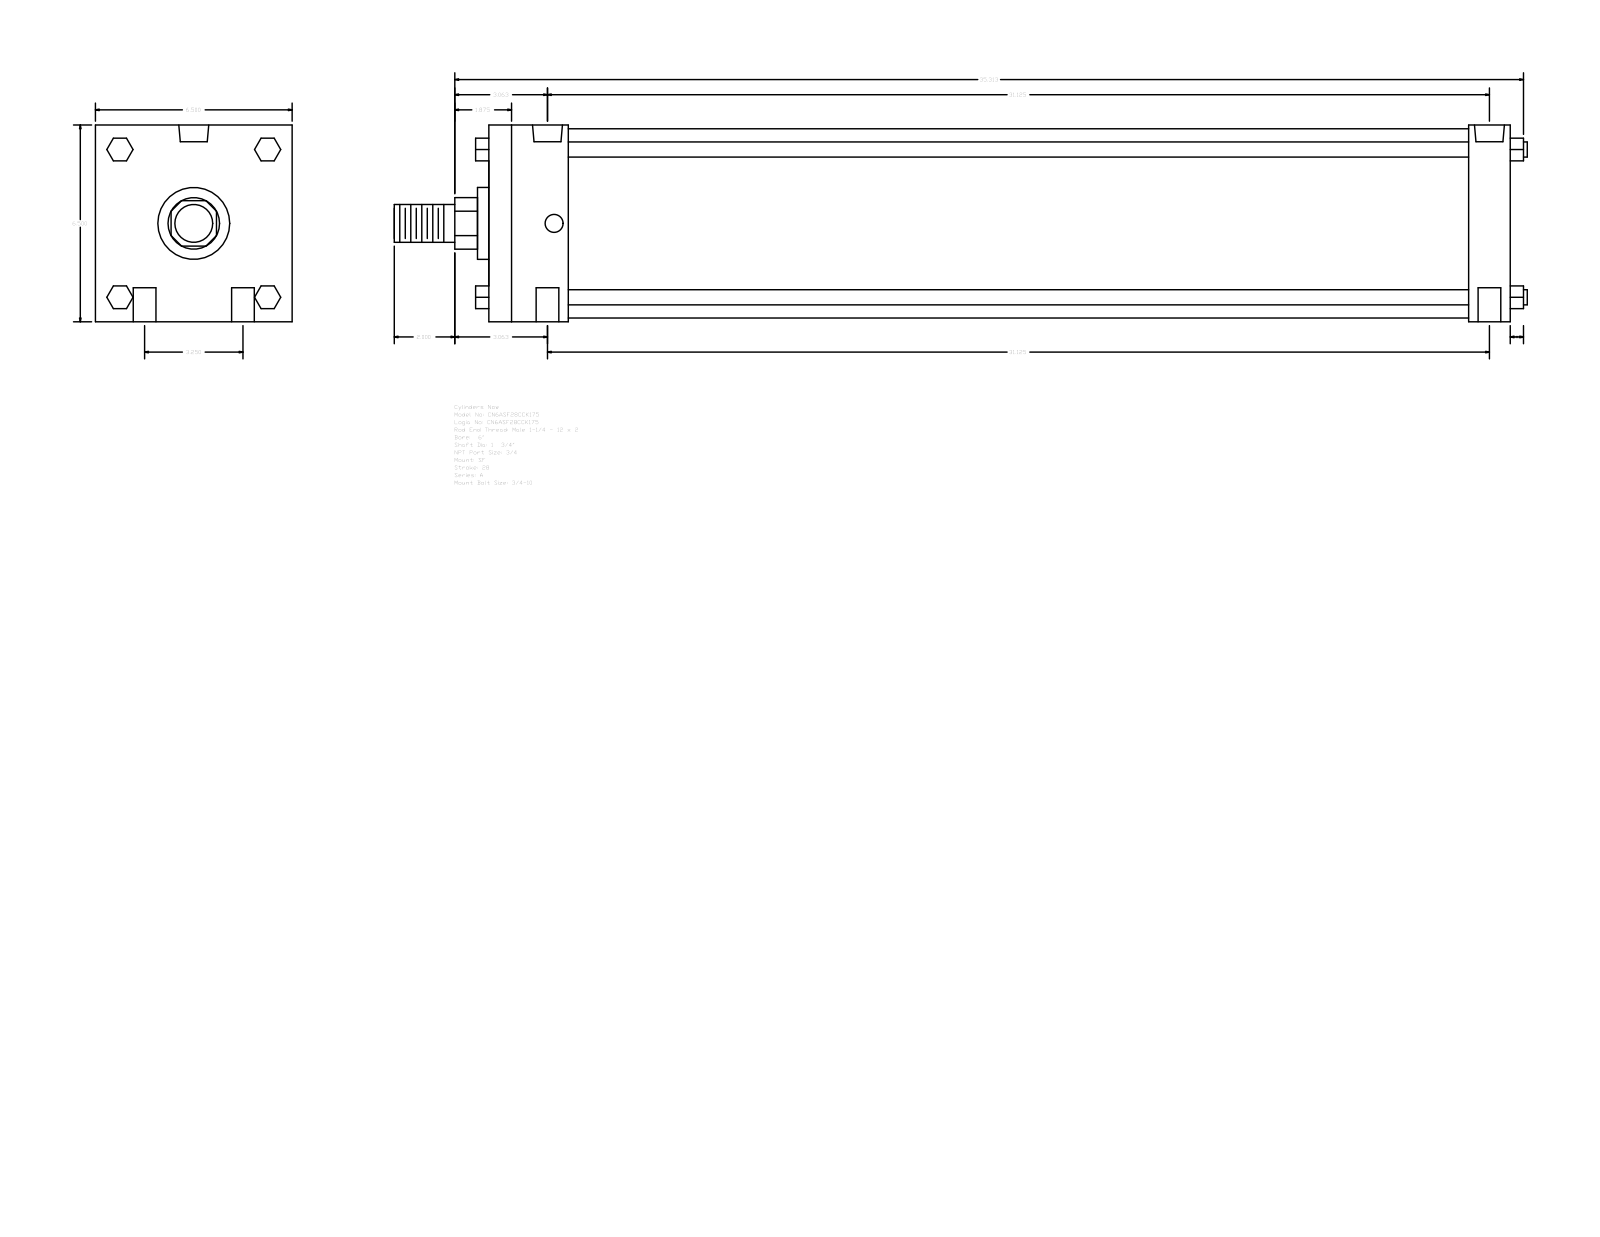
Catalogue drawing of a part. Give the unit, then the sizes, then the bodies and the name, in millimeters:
Units: millimetres
Overall size (bounding box): 950.91 × 165.1 × 165.1
Round holes (diameter × count): ⌀19.05 ×4, ⌀15.08 ×2, ⌀25.12 ×2
Round bosses / shafts (diameter × count): ⌀12.7 ×4, ⌀158.75 ×1, ⌀60.33 ×1, ⌀44.45 ×1, ⌀31.75 ×1
Partial cylindrical surfaces — rounded edges, fillets, slot ends (radius × count): R21.63 ×1
Main face-to-face distances: 165.1, 857.26, 66.68, 822.33, 34.93, 755.65, 790.58, 19.05, 61.97, 107.34
Hole centre spacings: 41.27, 791.65, 790.57, 82.54, 794.87, 779.45
Bodies: 0 solids, 124 faces (94 planar, 30 cylindrical, 0 other)
Part name (STEP PRODUCT): A_SF__0600_1.75
STEP written by: GSSL Pune (CONFIG_CONTROL_DESIGN)
